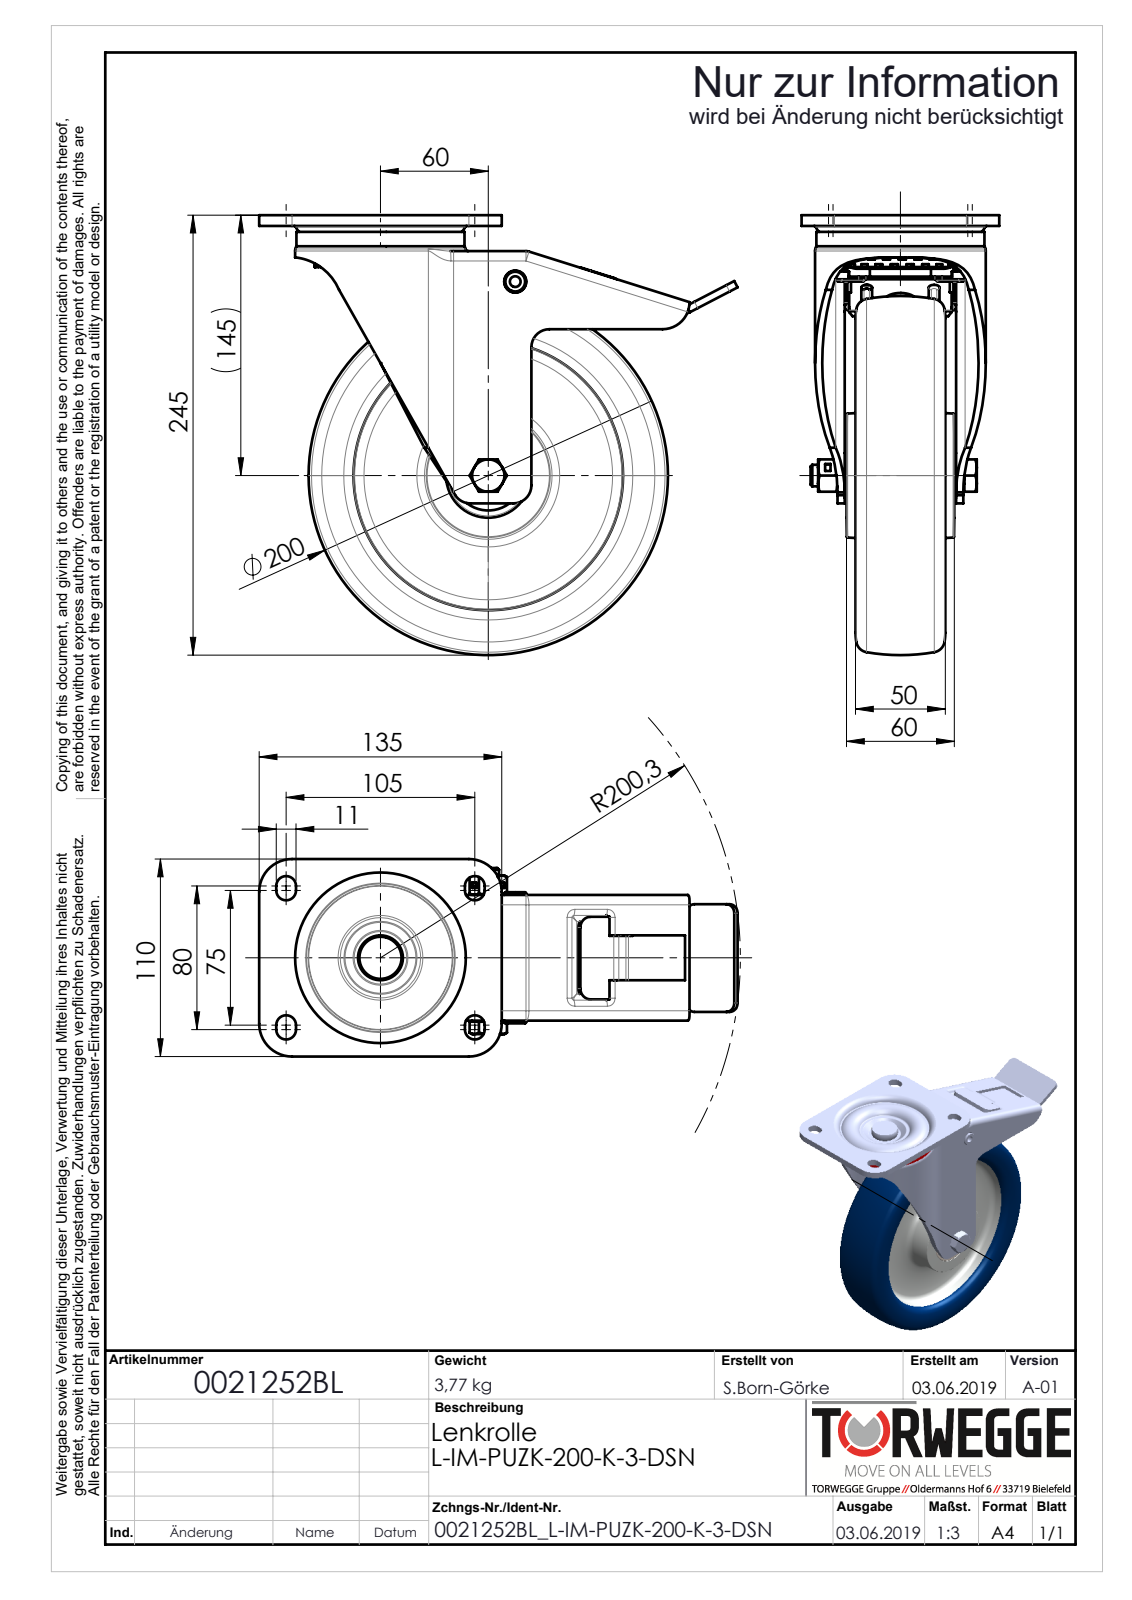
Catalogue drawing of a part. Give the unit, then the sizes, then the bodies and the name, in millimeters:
Units: millimetres
Overall size (bounding box): 266.25 × 243.37 × 110
Round holes (diameter × count): ⌀3.6 ×1, ⌀6 ×1, ⌀6.6 ×1, ⌀9.6 ×1, ⌀10.2 ×1, ⌀12 ×1, ⌀12.2 ×1, ⌀12.3 ×1, ⌀12.6 ×1, ⌀15.6 ×1, ⌀20 ×1, ⌀20.5 ×1
Round bosses / shafts (diameter × count): ⌀18 ×2, ⌀8 ×2, ⌀93.54 ×1, ⌀73.32 ×1, ⌀47 ×1, ⌀25 ×1, ⌀24 ×1, ⌀21.94 ×1
Partial cylindrical surfaces — rounded edges, fillets, slot ends (radius × count): R5.5 ×13, R4 ×10, R5 ×9, R1.5 ×8, R3 ×5, R0.75 ×4, R10 ×4, R18.29 ×4
Main face-to-face distances: 4, 66, 70, 62, 6, 1.5, 1, 13.5, 14, 47
Hole centre spacings: 109.04
Bodies: 0 solids, 964 faces (382 planar, 237 cylindrical, 345 other)
Part name (STEP PRODUCT): 0021252BL_L-IM-PUZK-200-K-3-DSN_(A-01)
STEP written by: SolidWorks 2018 (AUTOMOTIVE_DESIGN)
